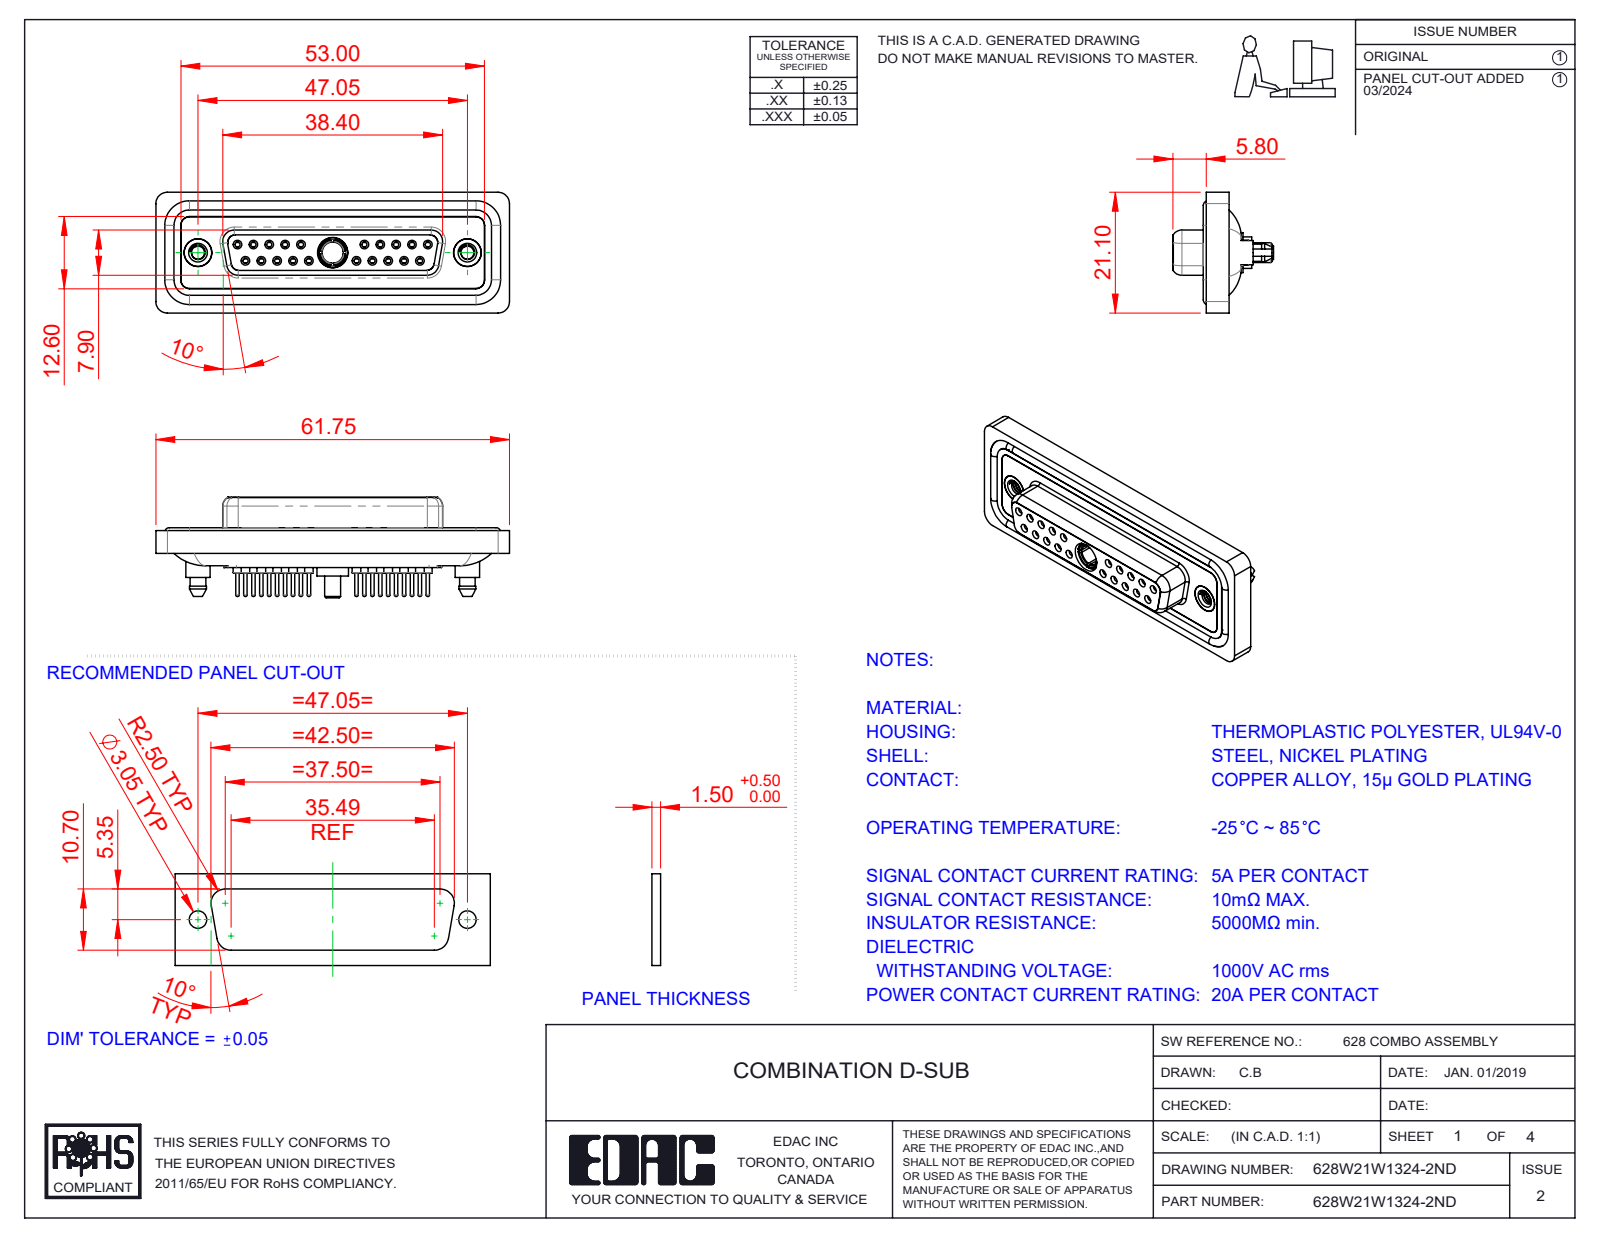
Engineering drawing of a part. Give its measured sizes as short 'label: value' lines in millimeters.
name: 628Combo Contact Row 2_24; 628Combo Housing_21W1; 628Combo Contact Row 1_24; Power Socket_20A S (+5 more)
written by: SolidWorks 2023 (CONFIG_CONTROL_DESIGN)
unit: mm
bodies: 29 solids, 1626 faces (450 planar, 639 cylindrical, 537 other)
size: 61.75 × 21.1 × 17.55
volume: 8 509 mm³; area: 14 341 mm²
holes: 20× ⌀0.9, 20× ⌀1.1, 20× ⌀1.5, 20× ⌀2, 10× ⌀1.6, 10× ⌀1.7, 3× ⌀4.85, 2× ⌀2.26, 2× ⌀4, 2× ⌀4.05, 2× ⌀5, 1× ⌀3.7
bosses: 20× ⌀2.2, 20× ⌀0.6, 14× ⌀1.6, 2× ⌀5.4, 2× ⌀4.95, 2× ⌀4.8, 2× ⌀4.25, 1× ⌀5.5
rounds: 24× R1.5, 18× R2, 10× R1.6, 8× R1.35, 4× R0.25, 4× R0.5, 4× R0.6, 4× R0.65
face distances: 0.4, 1.8, 7.45, 6.6, 5.65, 1.6, 0.5, 7.05, 2.9, 1.1
hole spacings: 3.16, 2.77, 5.54, 5.03, 8.31, 7.48, 16.62, 19.39
